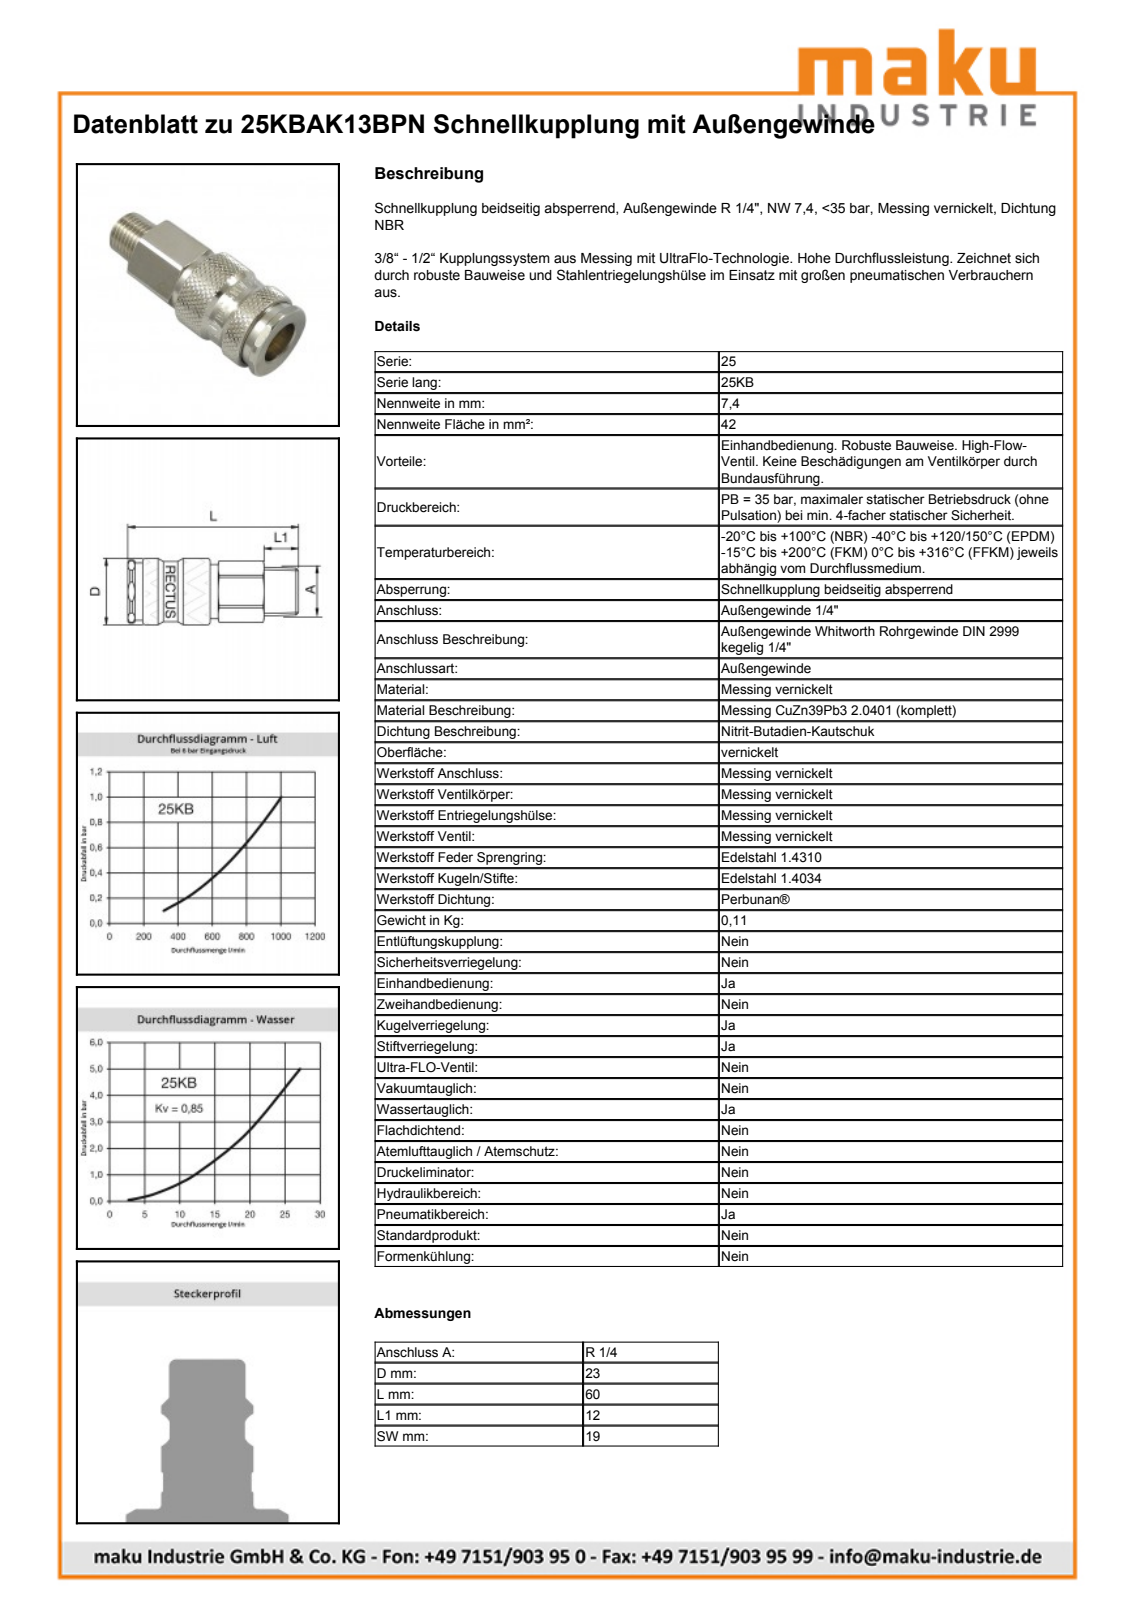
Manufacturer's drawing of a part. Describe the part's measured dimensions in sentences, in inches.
The part is named "D103443". Its 3-D file was written by "Autodesk Inventor 2011 (AUTOMOTIVE_DESIGN)". It is 2 solids with 552 faces: 213 planar, 62 cylindrical and 277 other. Overall it measures 2.356 by 0.911 by 0.911 inches. Its volume is 1.064 cubic inches and its surface area 11.64 square inches. Round holes: 1 of diameter 0.679, 1 of diameter 0.762, 1 of diameter 0.789. Round bosses or shafts: 1 of diameter 0.911, 1 of diameter 0.827, 1 of diameter 0.787, 1 of diameter 0.746, 1 of diameter 0.63. Partial cylindrical surfaces (rounded edges, fillets, slot ends): 1 of radius 0.409, 1 of radius 0.421, 1 of radius 0.433. The main face-to-face distances are 0.748, 1.884, 2.356, 0.472, 0.939, 0.945, 1.417, 1.132, 0.193, 0.752.
